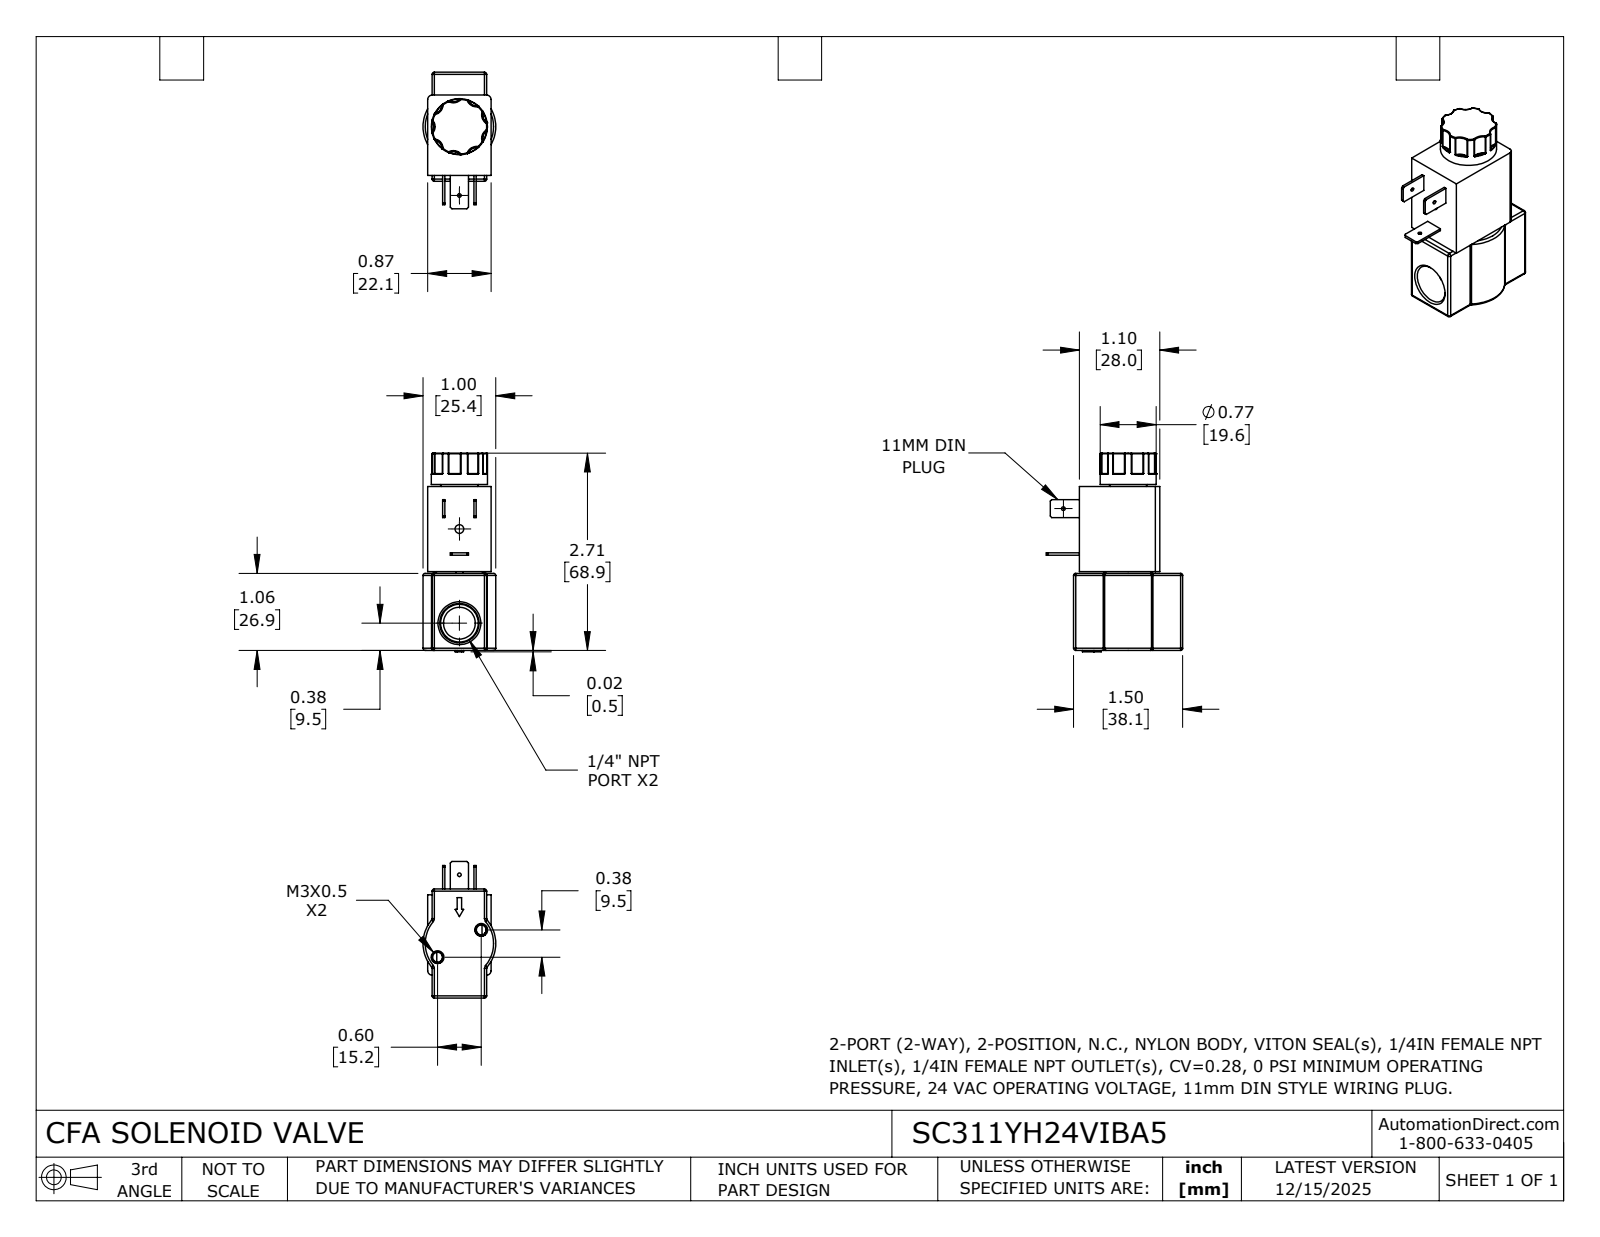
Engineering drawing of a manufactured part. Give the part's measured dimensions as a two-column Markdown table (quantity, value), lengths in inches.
| quantity | value |
| --- | --- |
| part name | SC311YH24VIBA5 |
| STEP written by | SolidWorks 2024 (CONFIG_CONTROL_DESIGN) |
| units | inches |
| bodies | 1 solid, 383 faces (62 planar, 117 cylindrical, 204 other) |
| overall size | 2.732 × 1.877 × 1 |
| volume | 2.397 in³ |
| surface area | 17.71 in² |
| round holes (diameter × count) | 0.05 × 2, 0.136 × 2, 0.12 × 1, 0.438 × 1 |
| round bosses / shafts (diameter × count) | 0.77 × 1 |
| partial cylindrical surfaces (radius × count) | 0.01 × 18, 0.03 × 16, 0.133 × 7, 0.06 × 2, 0.132 × 2, 0.295 × 2, 0.311 × 1, 0.5 × 1 |
| main face-to-face distances | 0.06, 0.81, 0.87, 1.104, 2.252, 1.06, 1.192, 0.75, 1.085, 0.025 |
| hole center spacings | 0.707, 0.815, 1.172, 1.293 |
